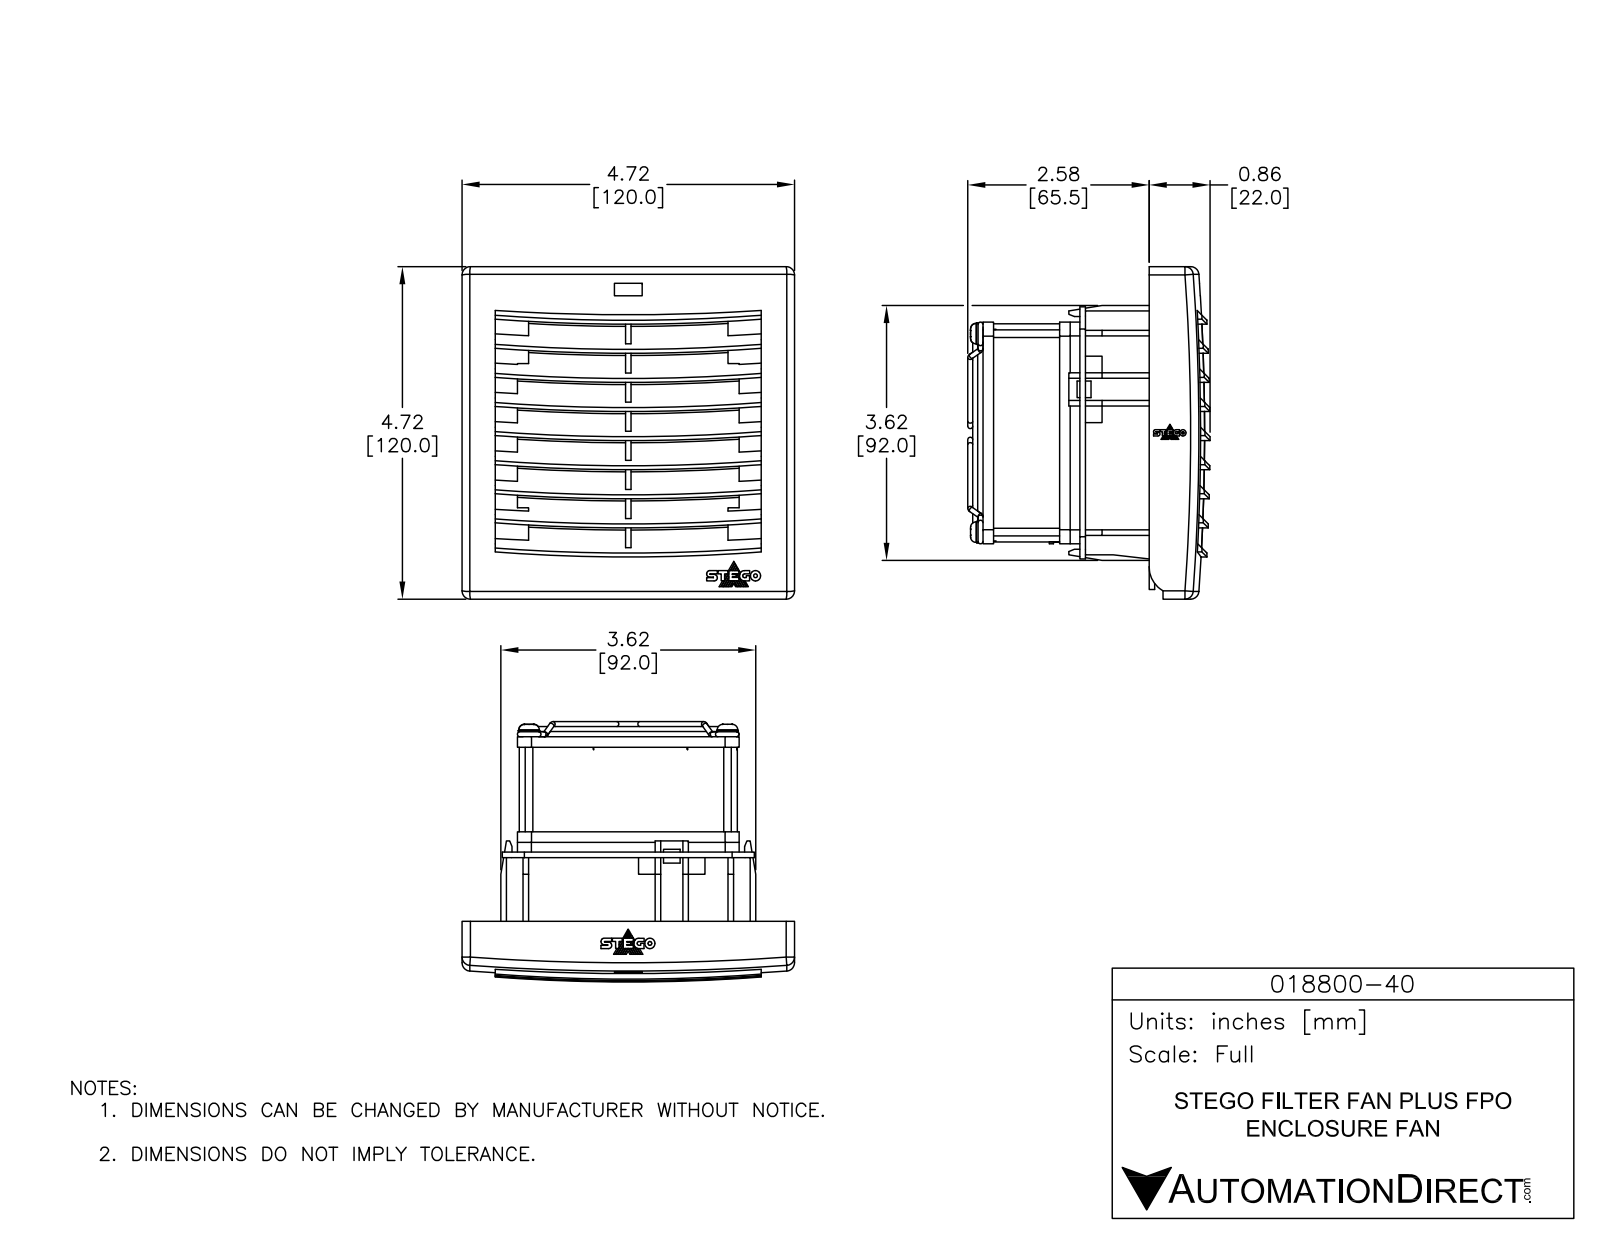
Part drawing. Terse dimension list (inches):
name: 018800-40
written by: SolidWorks 2018 (AUTOMOTIVE_DESIGN)
unit: in
bodies: 1 solid, 486 faces (273 planar, 205 cylindrical, 8 other)
size: 4.724 × 4.724 × 3.74
volume: 19.57 in³; area: 197.7 in²
holes: 4× ⌀0.217, 1× ⌀0.671, 1× ⌀1.153, 1× ⌀1.635, 1× ⌀1.996, 1× ⌀2.117, 1× ⌀2.496, 1× ⌀2.677, 1× ⌀3.079
bosses: 1× ⌀2.661, 1× ⌀2.274, 1× ⌀2.161, 1× ⌀1.792, 1× ⌀1.31, 1× ⌀0.937, 1× ⌀0.828
rounds: 15× R8.63, 5× R1.312, 4× R0.1, 4× R0.118, 1× R0.539, 1× R0.748, 1× R0.83, 1× R1.715
face distances: 0.316, 0.059, 0.091, 3.531, 0.632, 0.375, 0.551, 0.642, 4.083, 4.173
hole spacings: 2.082, 2.945, 4.165
